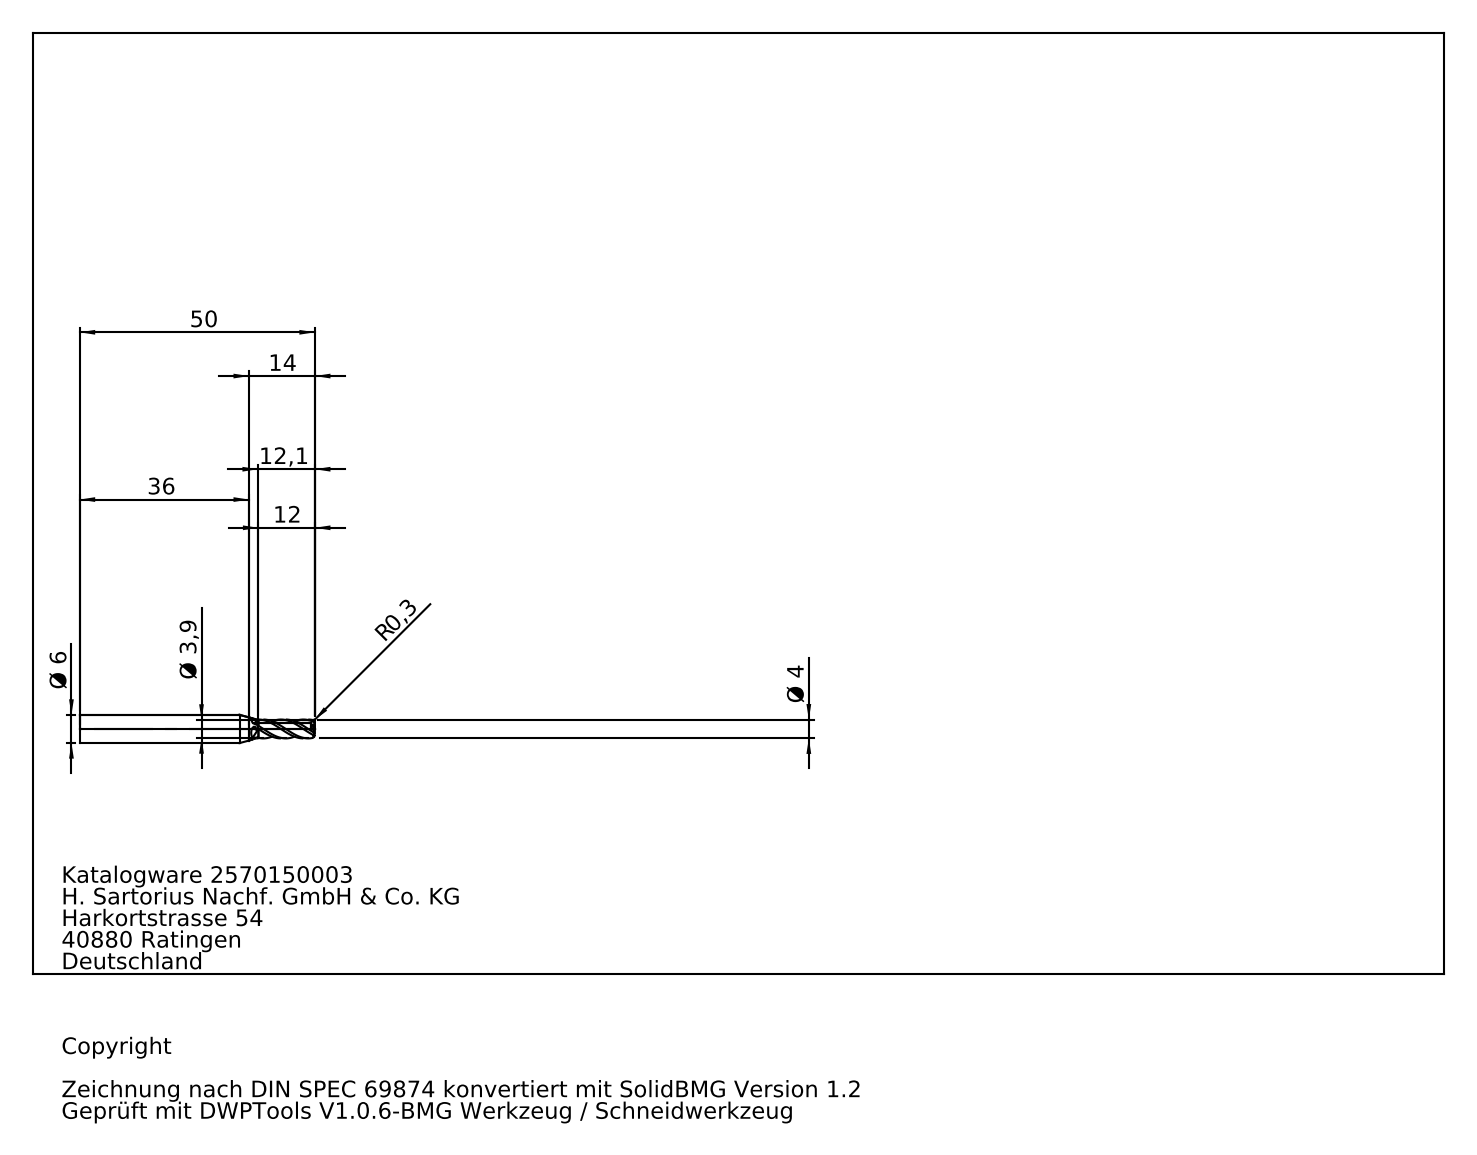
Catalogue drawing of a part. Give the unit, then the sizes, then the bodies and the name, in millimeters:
Units: millimetres
Overall size (bounding box): 50 × 6 × 6
Round holes (diameter × count): ⌀2.4 ×1
Round bosses / shafts (diameter × count): ⌀6 ×1, ⌀4 ×1
Partial cylindrical surfaces — rounded edges, fillets, slot ends (radius × count): R1.95 ×1
Main face-to-face distances: 49.25, 38, 11.25, 49.99, 11.99, 0.74
Volume: 1 134 mm³ · Surface area: 1 092 mm²
Bodies: 2 solids, 65 faces (14 planar, 23 cylindrical, 28 other)
Part name (STEP PRODUCT): 2570150003
STEP written by: SolidWorks 2010 (AUTOMOTIVE_DESIGN)
